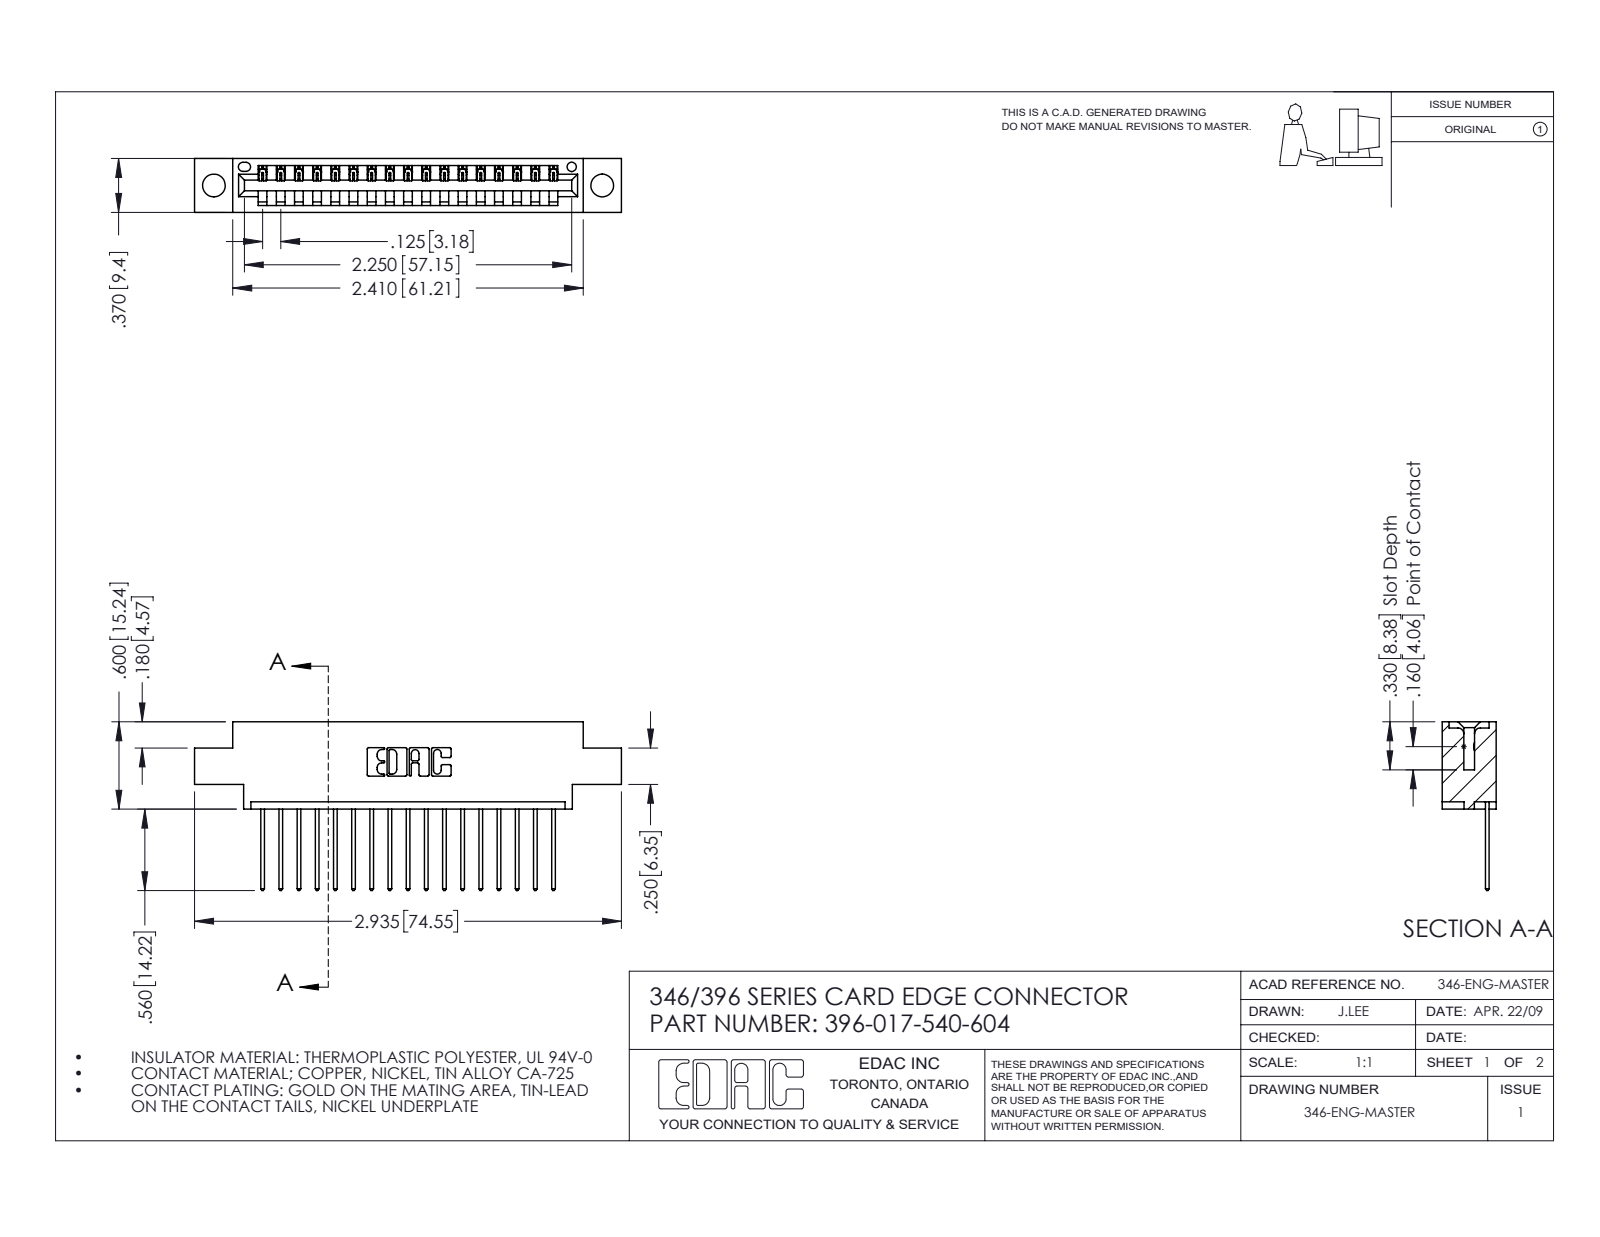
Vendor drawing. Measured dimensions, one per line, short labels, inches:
name: 345-292-001_345-293-140; 346 Part_0.170 Offset - 0.156 Dia-TH; 396-017-540-604
written by: SolidWorks 2016 (CONFIG_CONTROL_DESIGN)
unit: in
bodies: 18 solids, 1112 faces (760 planar, 352 cylindrical, 0 other)
size: 2.935 × 1.16 × 0.37
volume: 0.412 in³; area: 12.85 in²
holes: 2× ⌀0.156, 1× ⌀0.064
rounds: 34× R0.006, 34× R0.01, 22× R0.01, 6× R0.007, 6× R0.031, 3× R0.026, 2× R0.031, 2× R0.04
face distances: 0.048, 0.322, 0.37, 0.25, 0.072, 0.298, 0.025, 0.148, 0.222, 0.1
hole spacings: 0.246, 2.463, 2.67
